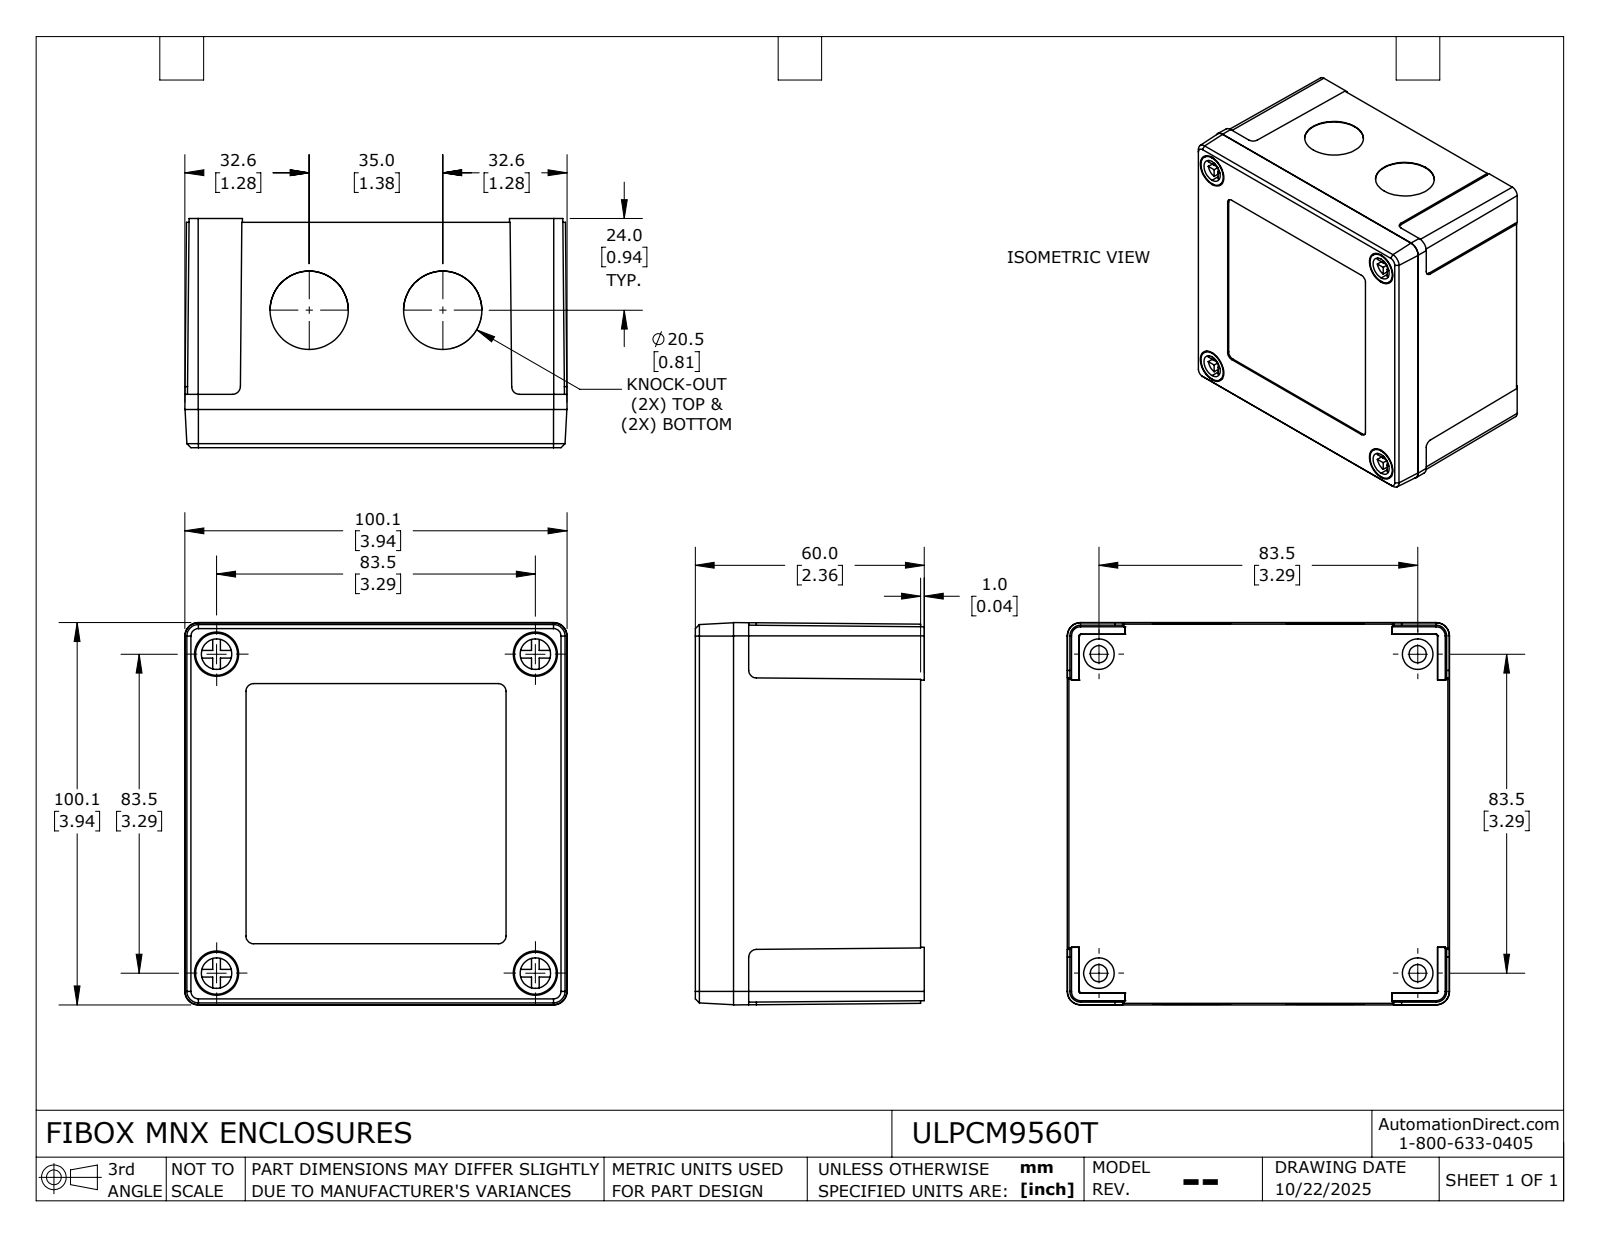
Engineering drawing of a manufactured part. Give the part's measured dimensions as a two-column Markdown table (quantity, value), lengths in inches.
| quantity | value |
| --- | --- |
| part name | ULPCM9560T_Default |
| STEP written by | SolidWorks 2024 (CONFIG_CONTROL_DESIGN) |
| units | inches |
| bodies | 6 solids, 510 faces (294 planar, 176 cylindrical, 40 other) |
| overall size | 3.941 × 3.941 × 2.362 |
| volume | 9.632 in³ |
| surface area | 147.4 in² |
| round holes (diameter × count) | 0.094 × 6, 0.118 × 6, 0.126 × 6, 0.157 × 6, 0.177 × 4, 0.315 × 4, 0.457 × 4, 0.807 × 4 |
| round bosses / shafts (diameter × count) | 0.315 × 6, 0.433 × 4, 0.283 × 4, 0.236 × 2 |
| partial cylindrical surfaces (radius × count) | 0.079 × 8, 0.056 × 6, 0.021 × 4, 0.03 × 4, 0.118 × 4, 0.197 × 4, 0.023 × 2 |
| main face-to-face distances | 0.165, 0.118, 2.232, 2.114, 2.205, 0.02, 2.303, 2.185, 0.071, 1.929 |
| hole center spacings | 0.803, 0.886, 1.159, 1.354, 1.461, 1.665, 1.824, 1.931 |
